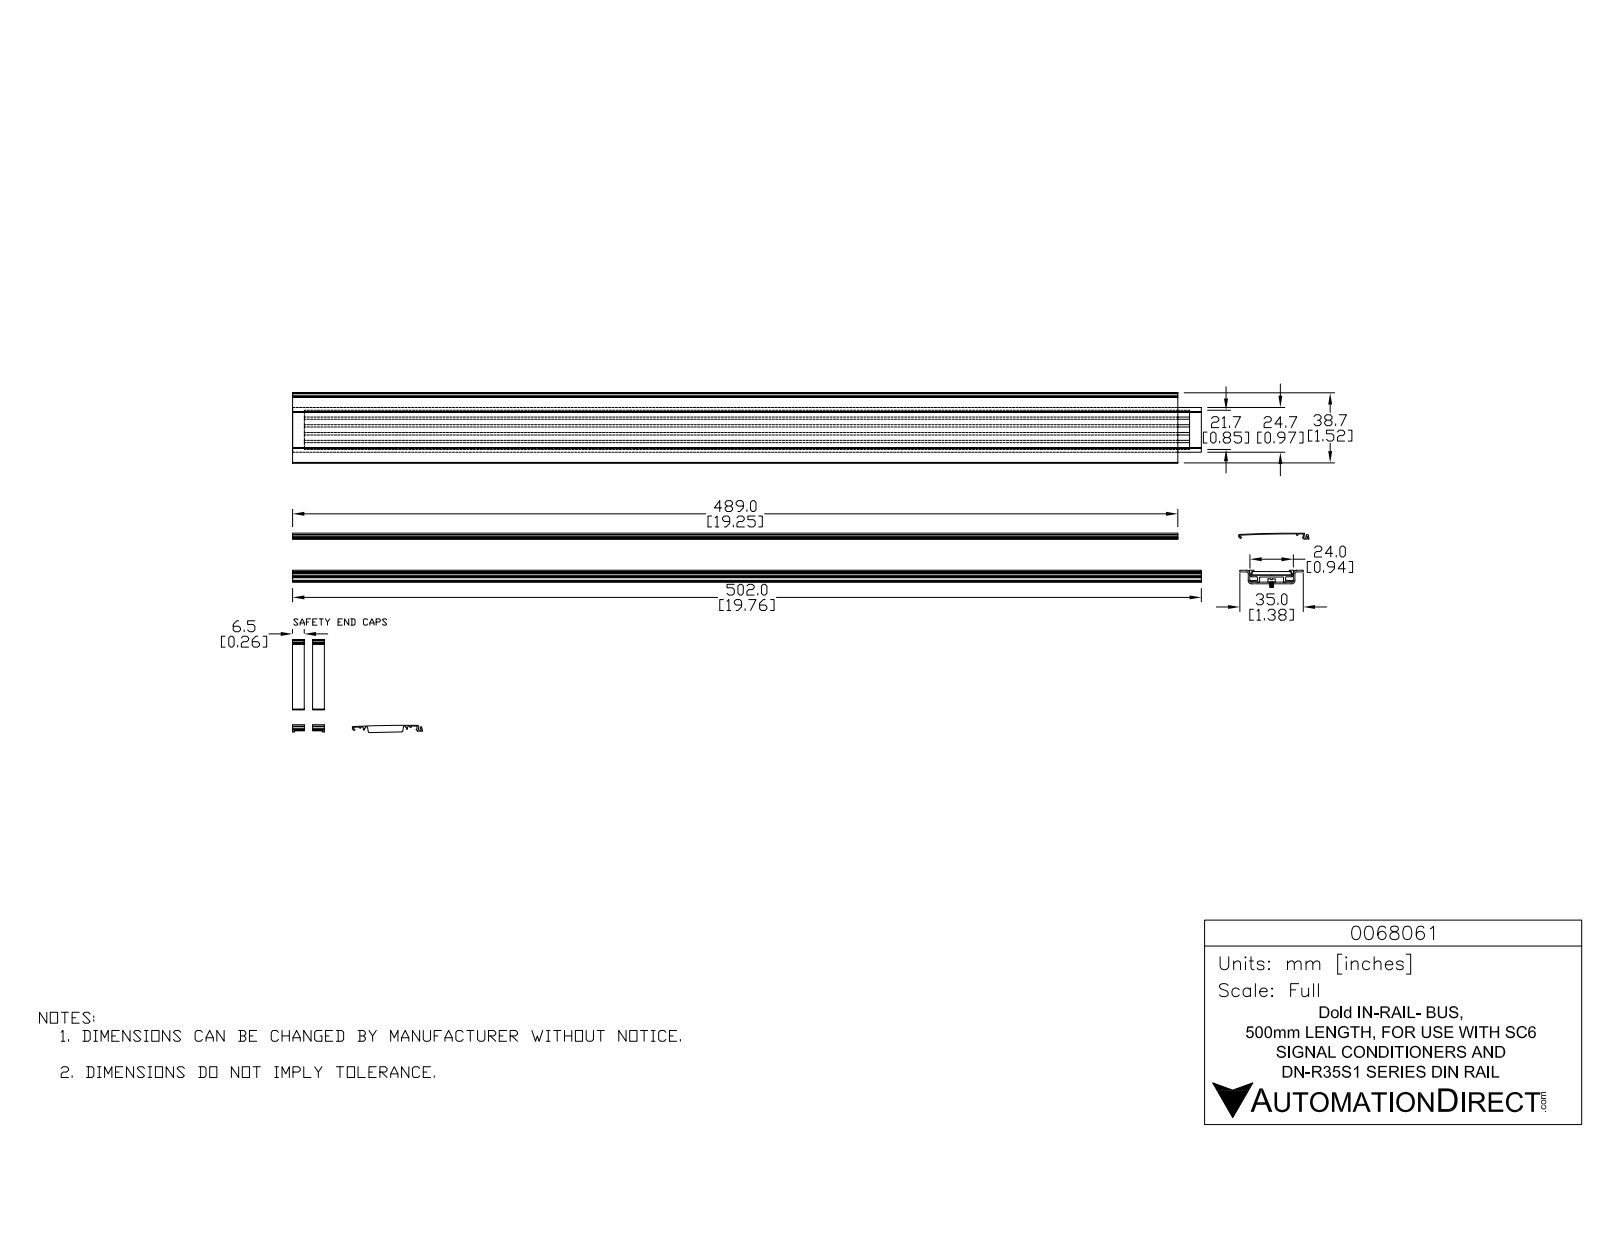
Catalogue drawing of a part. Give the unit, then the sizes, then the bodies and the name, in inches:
Units: inches
Overall size (bounding box): 27.854 × 1.525 × 0.687
Partial cylindrical surfaces — rounded edges, fillets, slot ends (radius × count): R0.01 ×14, R0.02 ×3, R0.029 ×3, R21.552 ×3, R0.028 ×2, R0.006 ×1, R0.006 ×1, R0.01 ×1
Main face-to-face distances: 0.072, 0.067, 0.039, 0.045, 0.111, 0.107, 0.068, 0.062, 0.143, 0.034
Volume: 2.986 in³ · Surface area: 180.6 in²
Bodies: 4 solids, 452 faces (378 planar, 74 cylindrical, 0 other)
Part name (STEP PRODUCT): POWER BUSS RAIL 500
STEP written by: SolidWorks 2017 (AUTOMOTIVE_DESIGN)
